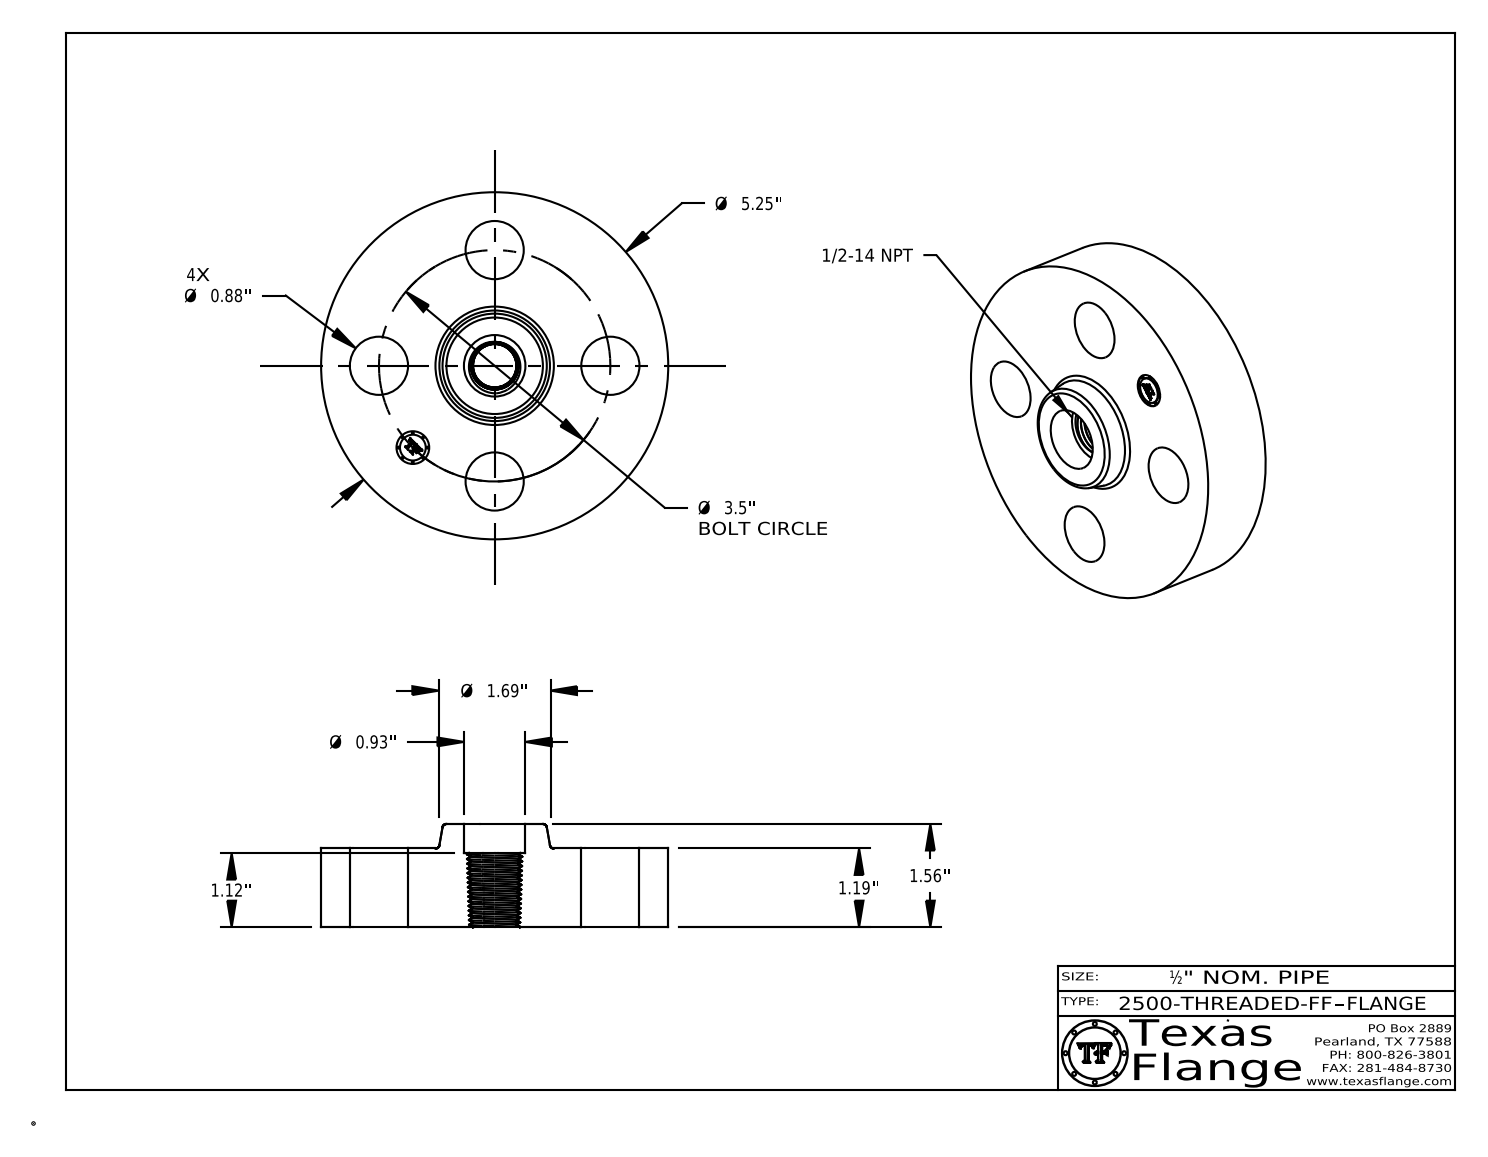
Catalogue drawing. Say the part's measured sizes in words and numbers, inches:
The part is named "2500-THREADED-FF". Its 3-D file was written by "CATIA V5 STEP AP214 (AUTOMOTIVE_DESIGN)". It is 1 solid with 570 faces: 369 planar, 32 cylindrical and 169 other. Overall it measures 5.25 by 5.25 by 1.56 inches. Its volume is 22.85 cubic inches and its surface area 78.04 square inches. Round holes: 4 of diameter 0.88, 1 of diameter 0.495, 1 of diameter 0.93. Round bosses or shafts: 8 of diameter 0.03, 1 of diameter 5.25, 1 of diameter 0.39. The main face-to-face distances are 1.19, 1.56, 0.37, 0.07, 1.12, 0.44, 1.175, 0.055, 0.015, 0.385. The hole center spacings are 1.75, 2.475, 1.339, 3.233, 3.5.
